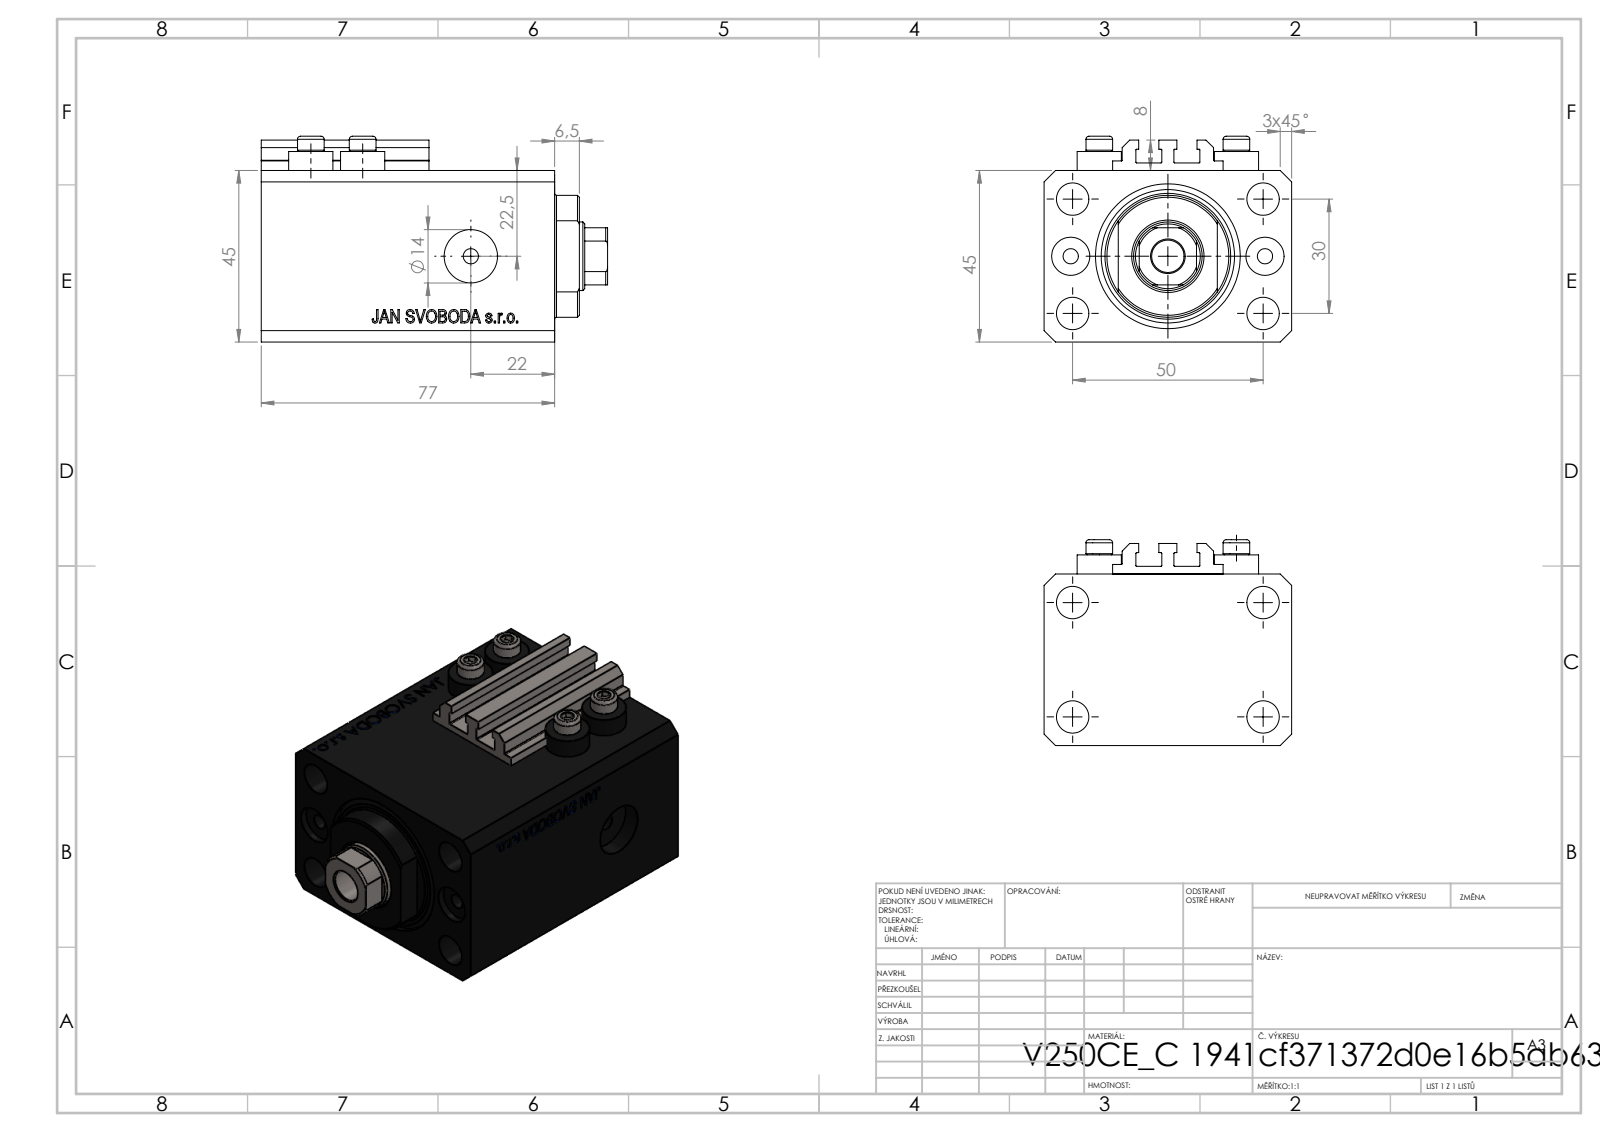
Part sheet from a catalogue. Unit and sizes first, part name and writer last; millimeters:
Units: millimetres
Overall size (bounding box): 90.9 × 65 × 54
Round holes (diameter × count): ⌀4 ×8, ⌀8.5 ×5, ⌀10 ×2, ⌀14 ×2, ⌀18 ×1, ⌀25 ×1, ⌀38 ×1
Round bosses / shafts (diameter × count): ⌀11.6 ×4, ⌀7 ×4
Partial cylindrical surfaces — rounded edges, fillets, slot ends (radius × count): R0.2 ×10, R8.5 ×1, R16 ×1
Main face-to-face distances: 45, 65, 51.9, 77, 25.1, 6.9, 70.1, 3, 47, 10
Hole centre spacings: 15.01, 29.15, 52.68, 13.6, 25.5, 30, 36, 38.48
Volume: 211 888 mm³ · Surface area: 59 424 mm²
Bodies: 8 solids, 1033 faces (503 planar, 86 cylindrical, 444 other)
Part name (STEP PRODUCT): ALLEN BOLT V250CE; V250CE_VC_C; V250CE_C_Body; V250CE_C_VCP
STEP written by: SolidWorks 2019 (CONFIG_CONTROL_DESIGN)
